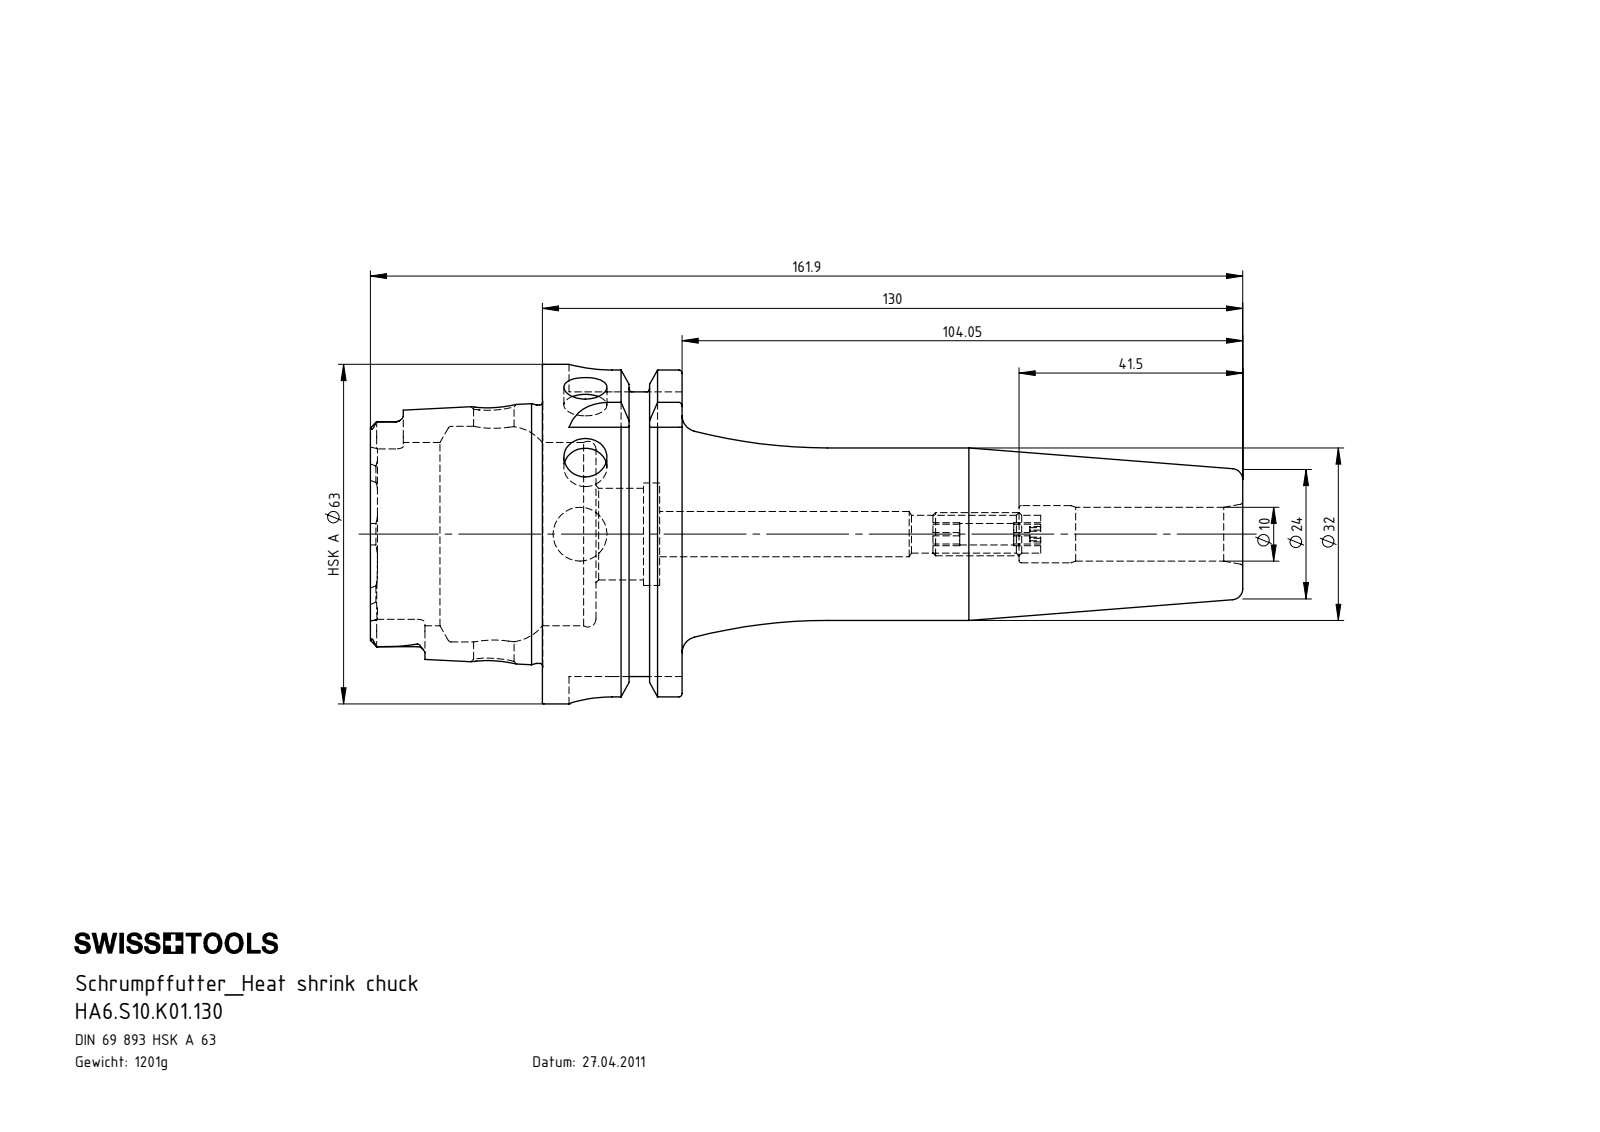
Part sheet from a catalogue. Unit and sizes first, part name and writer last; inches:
Units: inches
Overall size (bounding box): 6.374 × 2.48 × 2.48
Round holes (diameter × count): ⌀0.315 ×2, ⌀0.394 ×2, ⌀0.157 ×1, ⌀0.276 ×1, ⌀0.295 ×1, ⌀0.331 ×1, ⌀0.417 ×1, ⌀0.669 ×1, ⌀0.748 ×1, ⌀1.339 ×1, ⌀1.575 ×1
Round bosses / shafts (diameter × count): ⌀2.48 ×1, ⌀2.163 ×1, ⌀1.887 ×1, ⌀1.26 ×1, ⌀0.315 ×1
Partial cylindrical surfaces — rounded edges, fillets, slot ends (radius × count): R0.055 ×6, R0.113 ×4, R0.315 ×4
Main face-to-face distances: 1.022, 0.63, 0.392, 1.256, 1.648, 2.278, 2.079, 0.858, 0.467, 2.114
Volume: 9.334 in³ · Surface area: 54.7 in²
Bodies: 2 solids, 238 faces (82 planar, 61 cylindrical, 95 other)
Part name (STEP PRODUCT): HA6-S10.K01.130; ERU-AN3.K01.020_A; HA6-S10.K01.130_A_Fertigbearbeitung
STEP written by: SolidWorks 2012 (AUTOMOTIVE_DESIGN)
